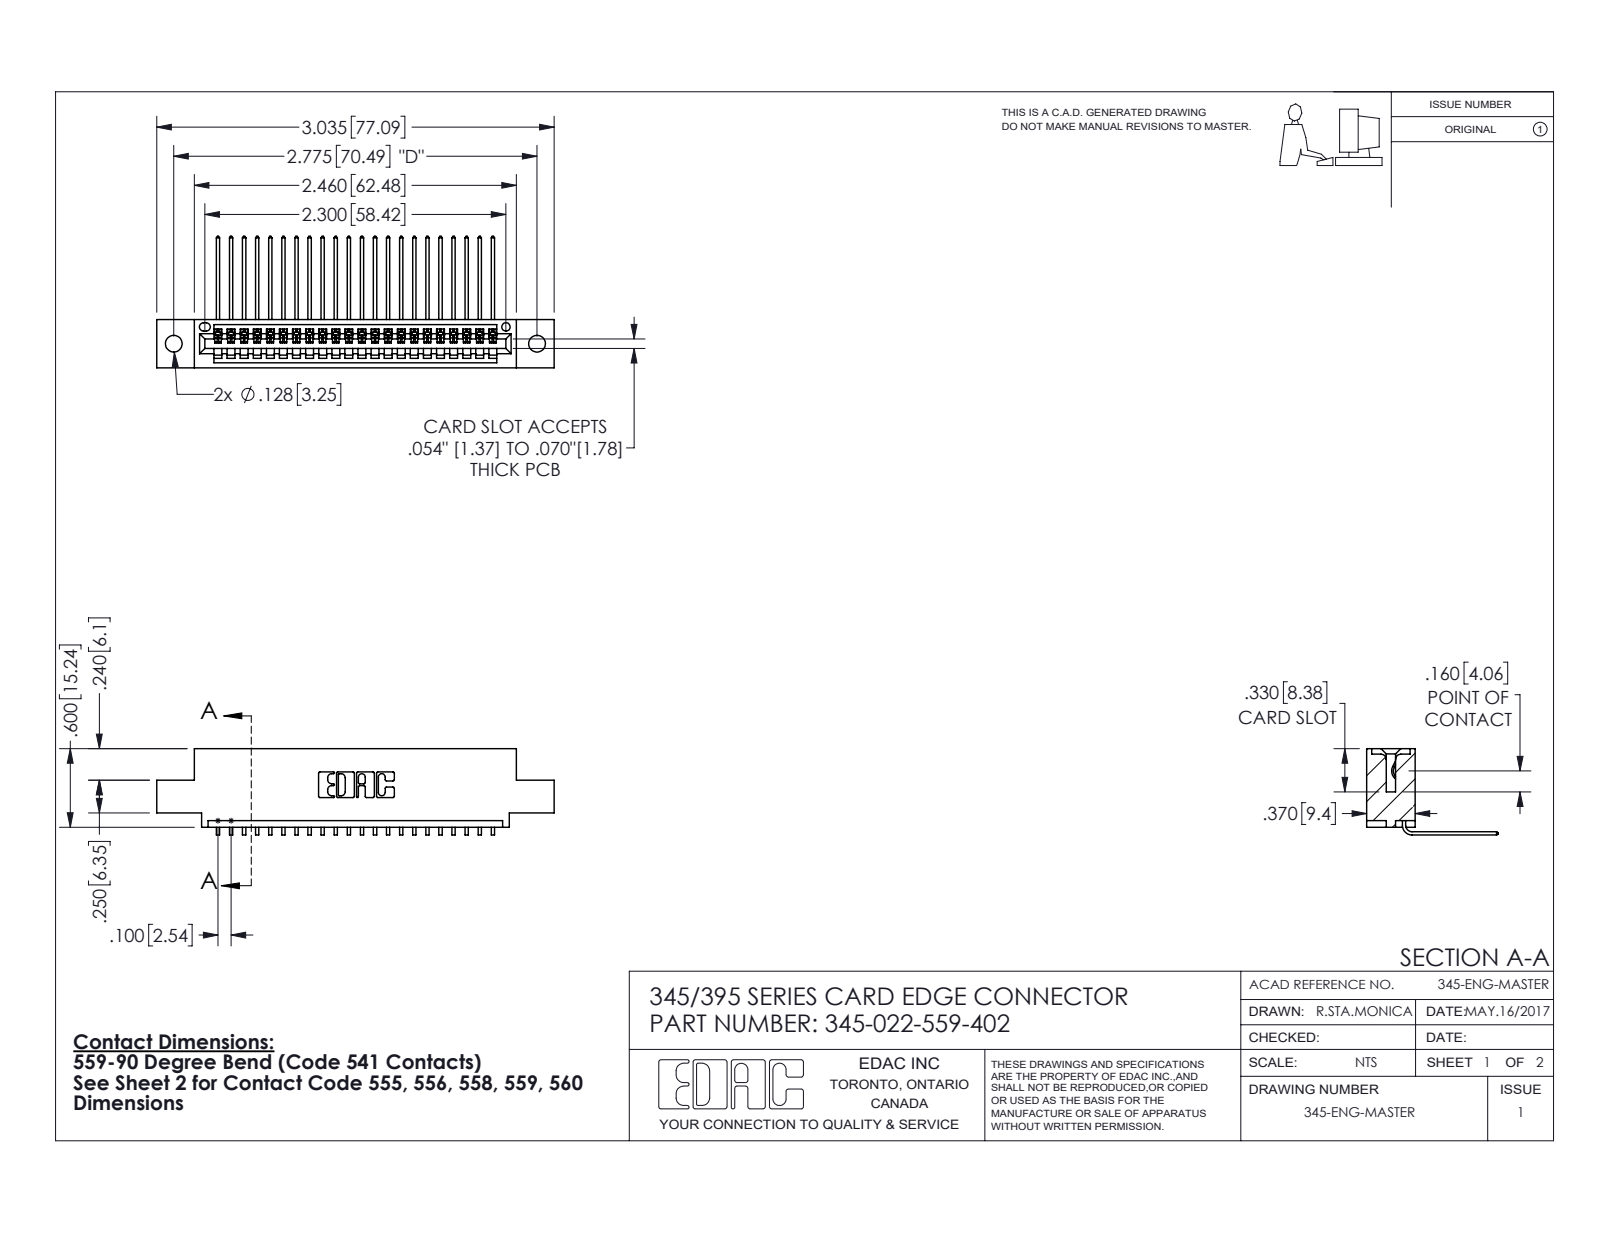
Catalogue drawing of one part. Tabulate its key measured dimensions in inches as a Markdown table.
| quantity | value |
| --- | --- |
| part name | 345-022-559-402; 345 Part_0.110 Offset - 0.128 Dia; 345-292-001_558 559 Tail - 1 |
| STEP written by | SolidWorks 2016 (CONFIG_CONTROL_DESIGN) |
| units | inches |
| bodies | 23 solids, 1450 faces (1008 planar, 442 cylindrical, 0 other) |
| overall size | 3.035 × 1.005 × 0.659 |
| volume | 0.435 in³ |
| surface area | 14.62 in² |
| round holes (diameter × count) | 0.128 × 2, 0.064 × 1 |
| partial cylindrical surfaces (radius × count) | 0.006 × 44, 0.01 × 22, 0.007 × 6, 0.031 × 6, 0.026 × 3, 0.031 × 2, 0.04 × 2, 0.014 × 1 |
| main face-to-face distances | 0.072, 0.298, 0.37, 0.2, 0.098, 0.272, 0.025, 0.225, 0.149, 0.072 |
| hole center spacings | 0.27, 2.541, 2.775 |
